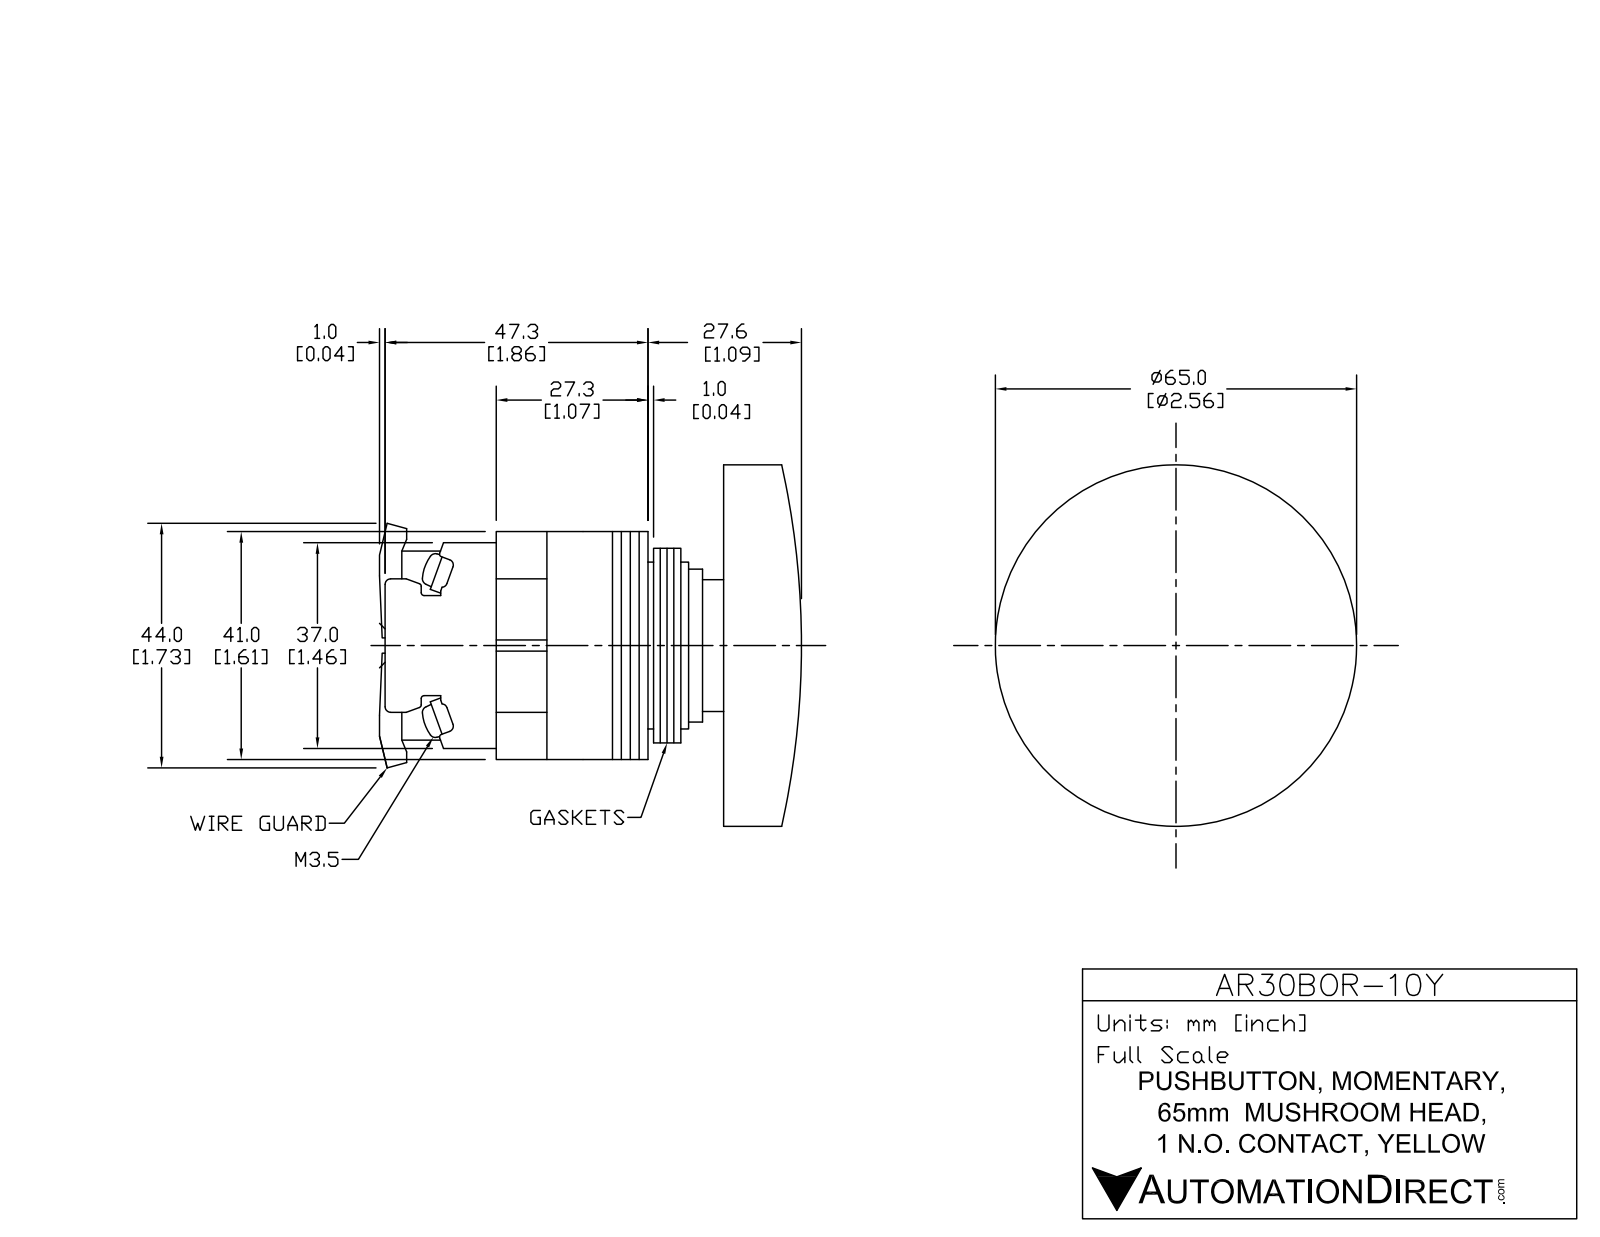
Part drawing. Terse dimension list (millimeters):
name: AR30B0R-10Y
written by: SolidWorks 2017 (AUTOMOTIVE_DESIGN)
unit: mm
bodies: 14 solids, 246 faces (140 planar, 92 cylindrical, 14 other)
size: 76 × 65 × 65
volume: 74 048 mm³; area: 37 582 mm²
holes: 4× ⌀3, 1× ⌀24, 1× ⌀30, 1× ⌀60
bosses: 2× ⌀5, 1× ⌀65, 1× ⌀40, 1× ⌀35, 1× ⌀29.8
rounds: 10× R5, 8× R0.5, 4× R1.75, 4× R3, 2× R2
face distances: 1.6, 3.2, 16, 21, 5, 41, 4.8, 15.99, 5.01, 25
hole spacings: 21.92, 31, 43.84
